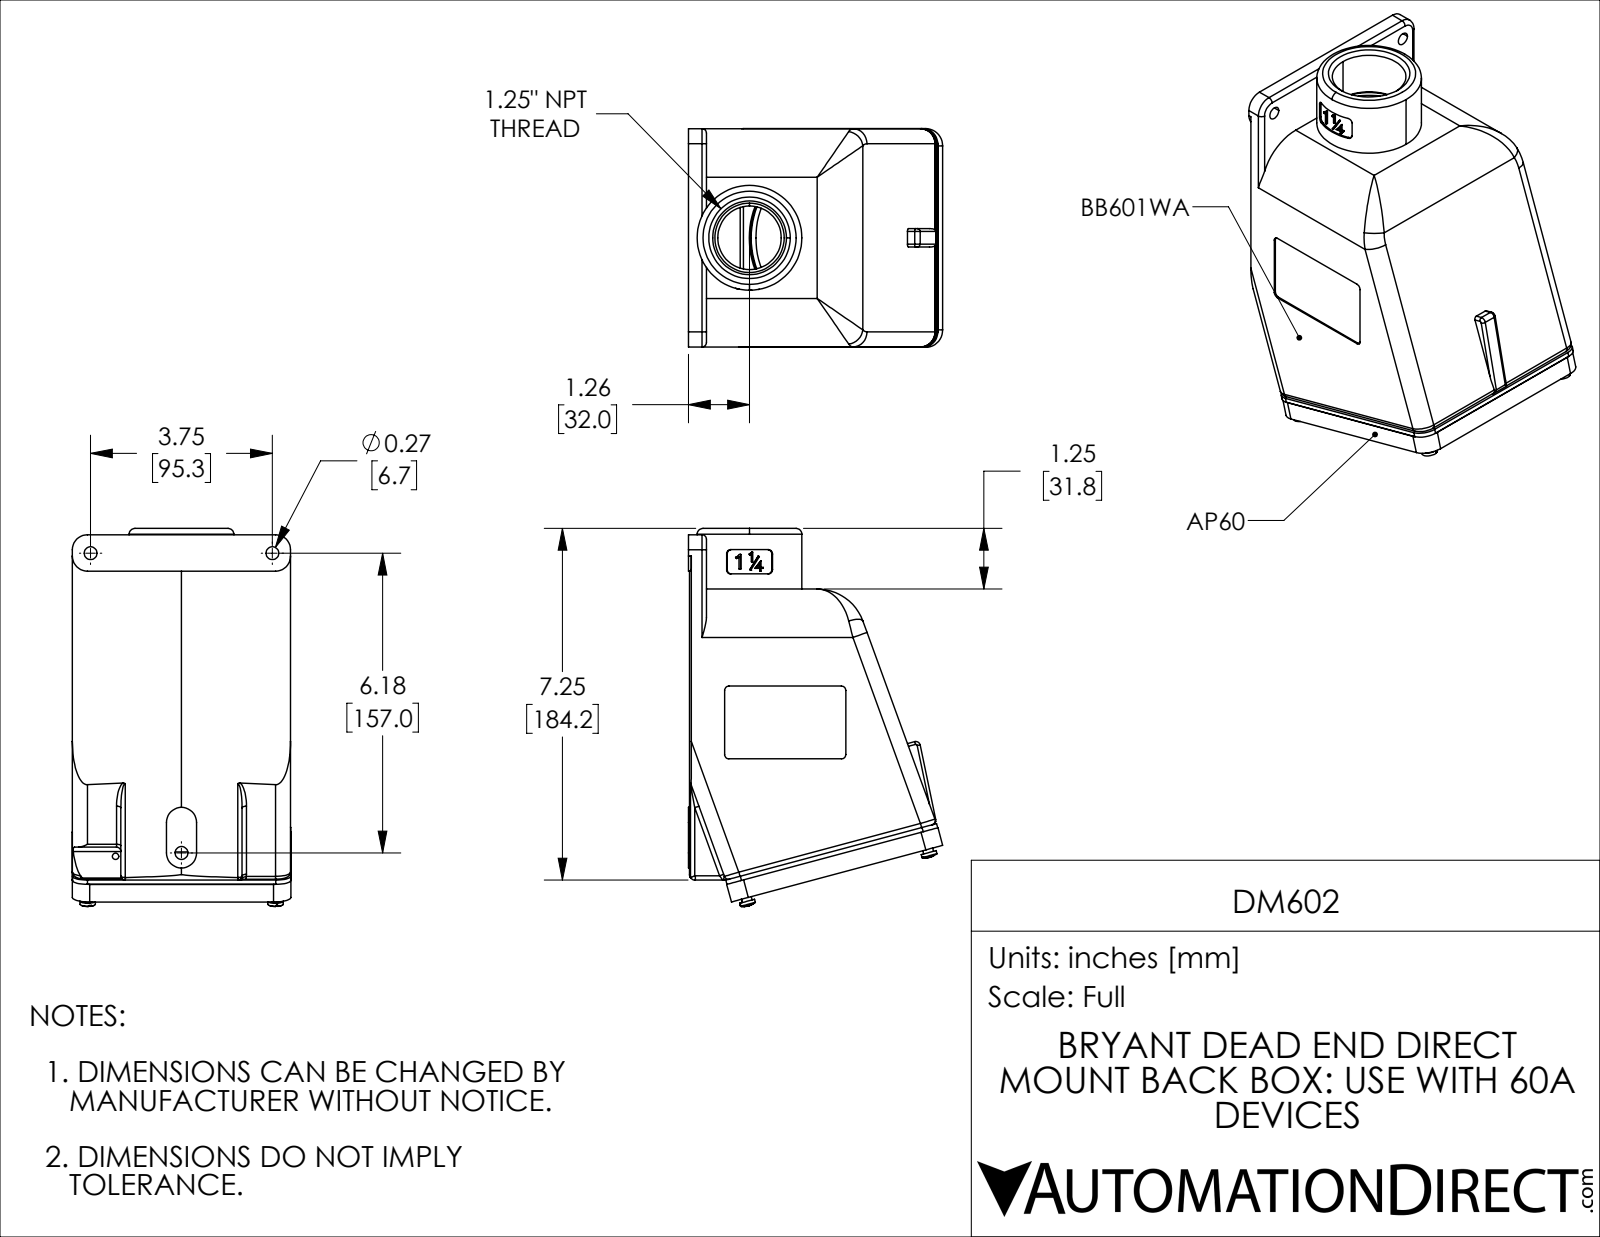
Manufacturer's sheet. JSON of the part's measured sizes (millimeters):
{"part_name": "BB601WA; AP60; DM602", "step_written_by": "SolidWorks 2021 (CONFIG_CONTROL_DESIGN)", "units": "millimeters", "bodies": {"solids": 7, "faces": 544, "planar": 215, "cylindrical": 251, "other": 78}, "overall_size": [198, 133.1, 114.6], "volume_mm3": 467200, "surface_area_mm2": 192500, "round_holes": [[5.5, 8], [3.7, 4], [5.6, 4], [9.9, 4], [4.4, 2], [4.4, 2], [6.7, 2], [14.2, 2], [3.3, 1], [6.7, 1], [33.3, 1], [38.6, 1]], "round_bosses_or_shafts": [[8.1, 4], [5.4, 4], [54.9, 1]], "partial_cylinders_radius": [[2.3, 40], [7.9, 14], [0.8, 6], [1.5, 4], [6.4, 4], [9.1, 4], [20.6, 3], [25.4, 3]], "face_to_face_distances": [4.8, 109.5, 104.6, 114.3, 9.5, 2.3, 11.8, 109.1, 11.8, 2.3], "hole_center_spacings": [98.5, 98.4, 12.6, 88, 92.3, 98.6, 126.9, 69.6]}
